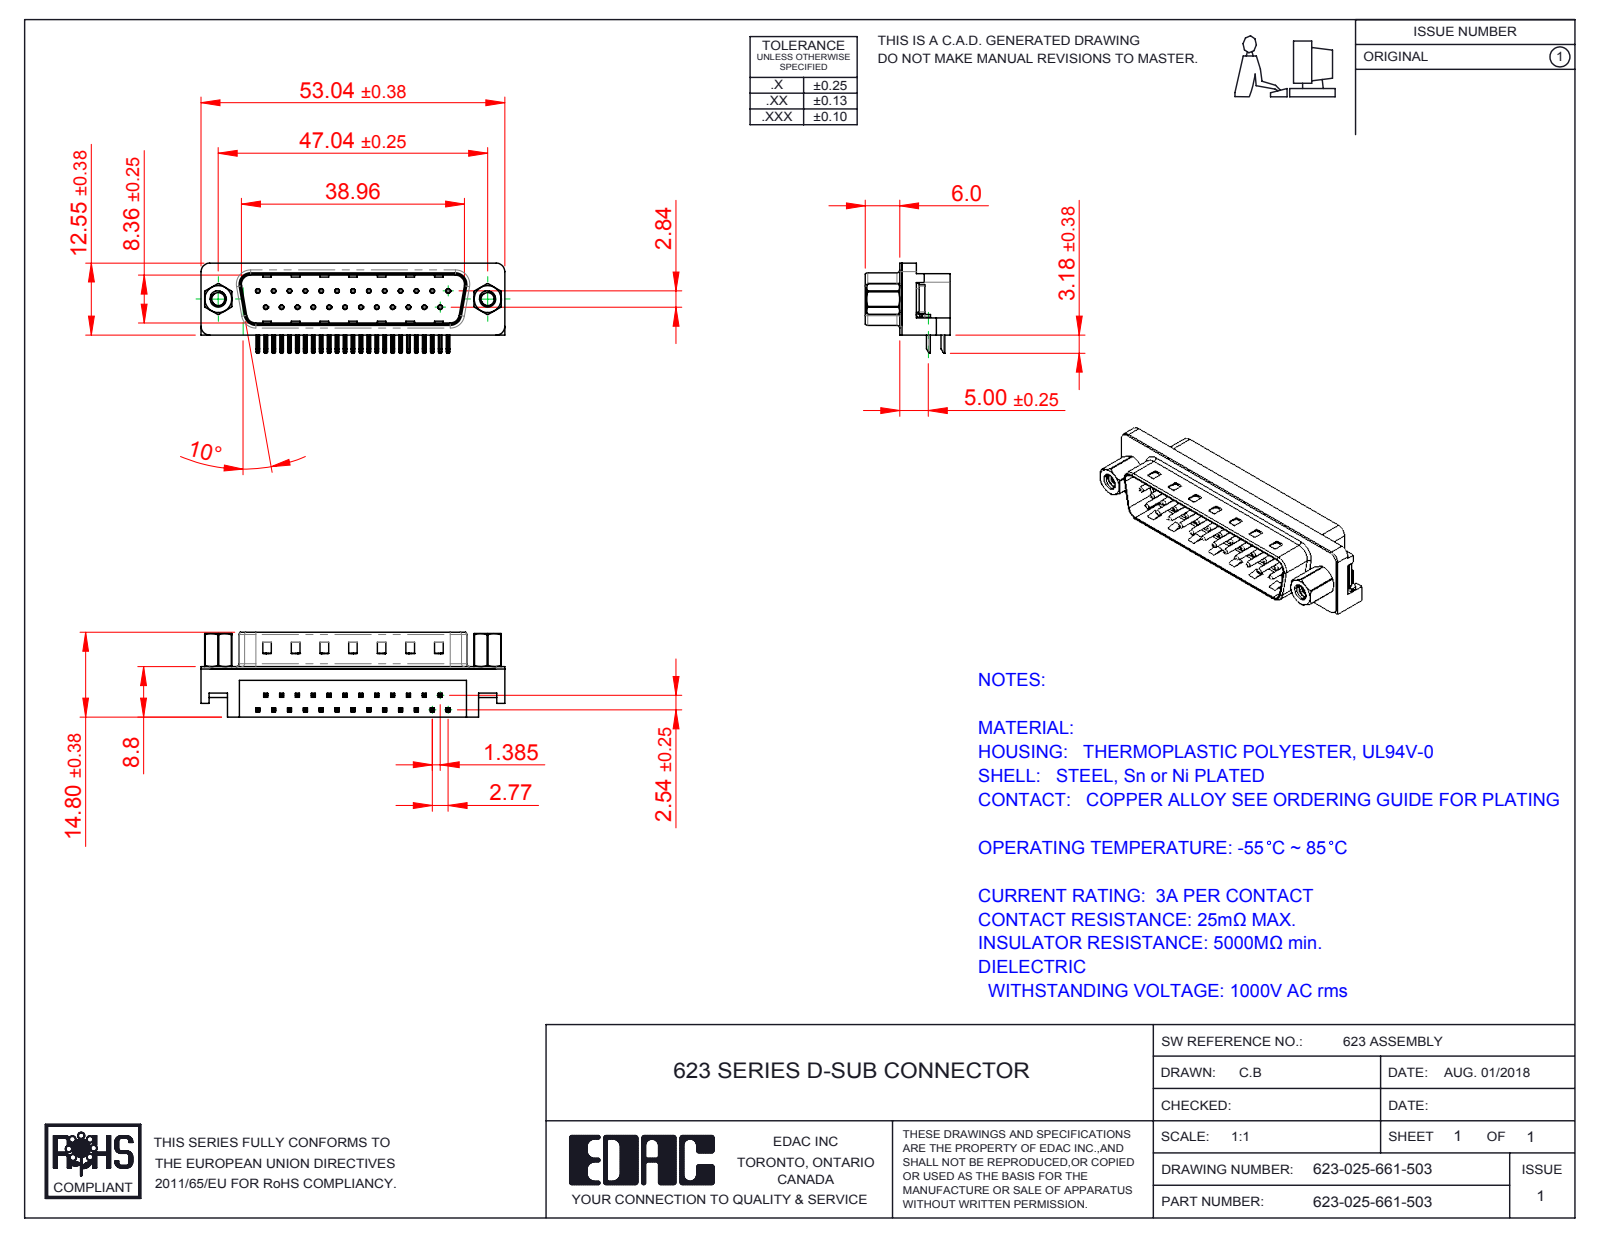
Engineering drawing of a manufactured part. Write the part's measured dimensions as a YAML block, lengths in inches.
part_name: "623 4-40 Threaded Rivet; 623 Shell_25 Socket; 623 Housing_25 Socket; 623 4-40 Hex Standoff 5 (+4 more)"
step_written_by: "SolidWorks 2016 (CONFIG_CONTROL_DESIGN)"
units: inches
bodies: {solids: 33, faces: 2377, planar: 1427, cylindrical: 717, other: 233}
overall_size: [2.088, 0.619, 0.583]
volume: 0.301
surface_area: 11.14
round_holes:
  - {diameter: 0.014, count: 25}
  - {diameter: 0.031, count: 25}
  - {diameter: 0.089, count: 2}
  - {diameter: 0.09, count: 2}
  - {diameter: 0.157, count: 2}
  - {diameter: 0.189, count: 2}
  - {diameter: 0.197, count: 2}
round_bosses_or_shafts:
  - {diameter: 0.03, count: 25}
  - {diameter: 0.193, count: 2}
  - {diameter: 0.187, count: 2}
  - {diameter: 0.154, count: 2}
  - {diameter: 0.11, count: 2}
partial_cylinders:
  - {radius: 0.01, count: 108}
  - {radius: 0.005, count: 50}
  - {radius: 0.039, count: 16}
  - {radius: 0.02, count: 9}
  - {radius: 0.059, count: 7}
  - {radius: 0.035, count: 4}
  - {radius: 0.063, count: 4}
  - {radius: 0.079, count: 4}
face_to_face_distances: [0.016, 0.331, 0.083, 0.067, 0.345, 0.412, 0.428, 0.346, 0.407, 0.232]
hole_center_spacings: [0.124, 0.109, 0.436, 0.218, 0.327, 0.198, 0.545, 0.294]
